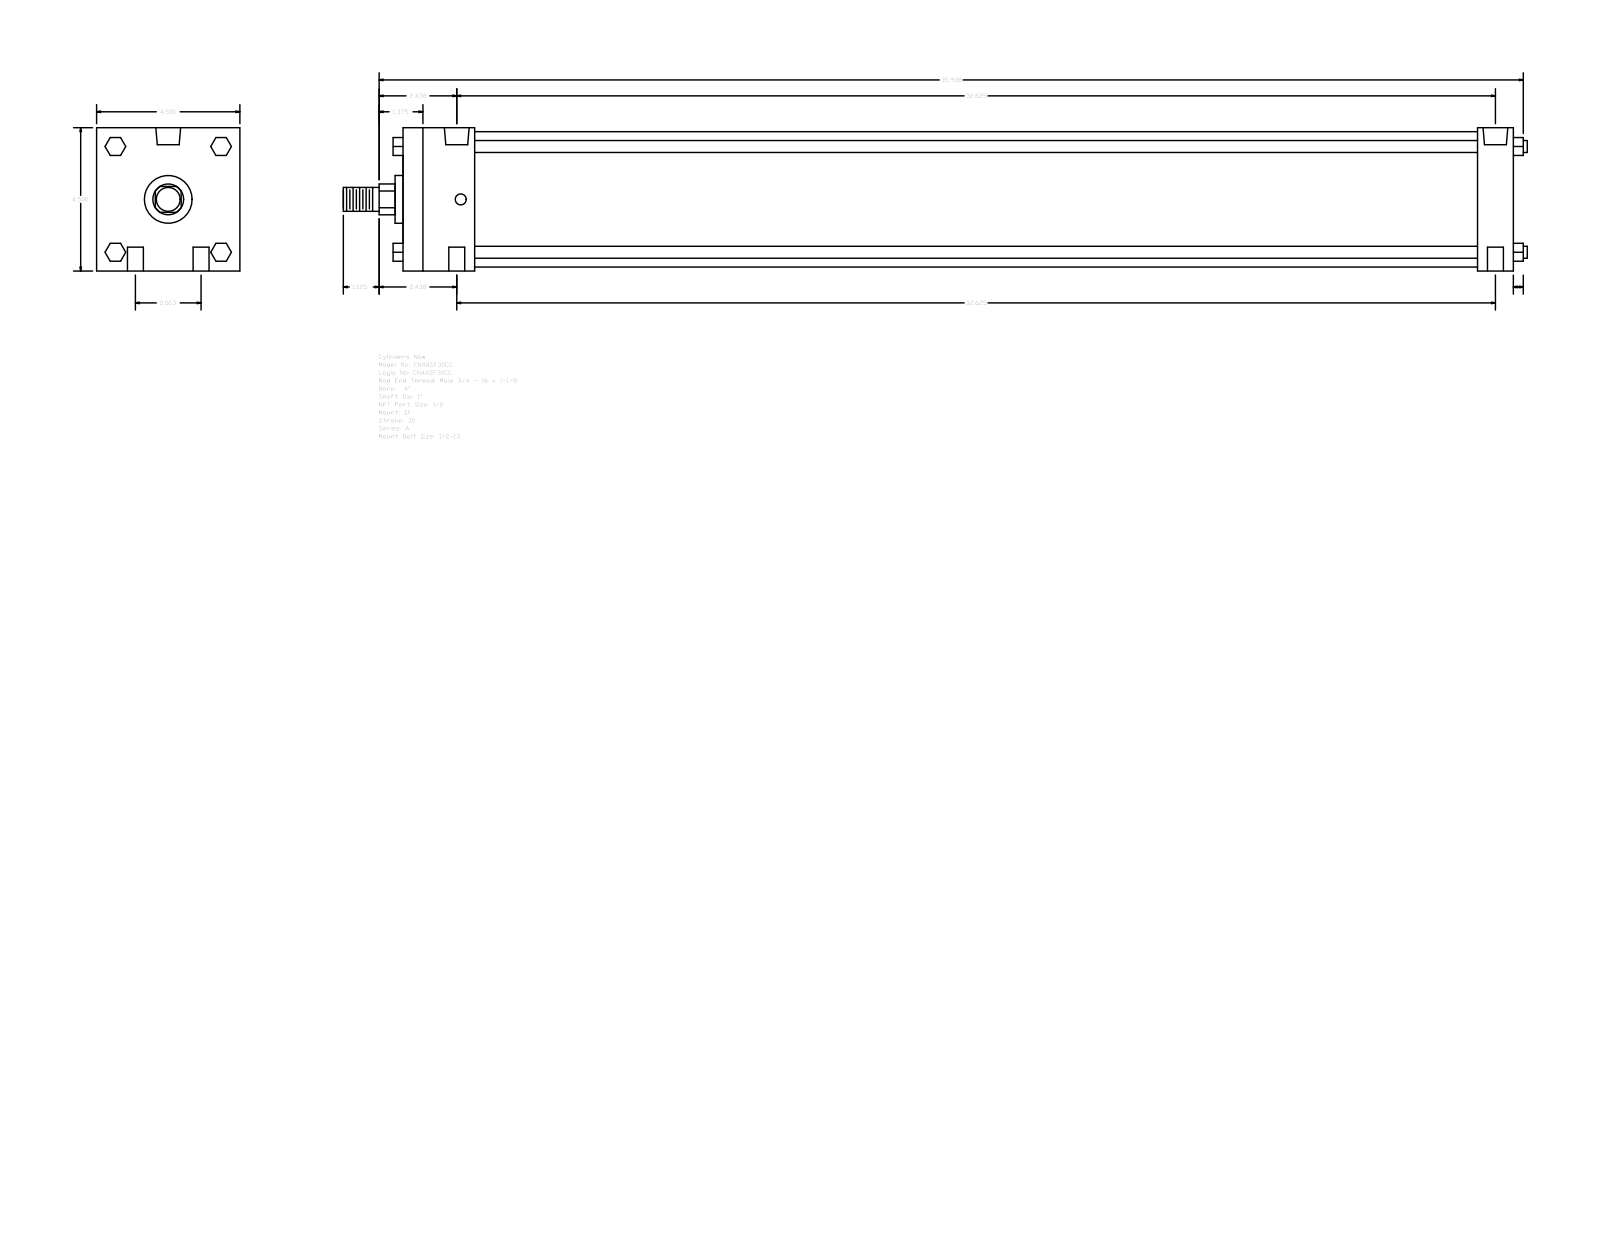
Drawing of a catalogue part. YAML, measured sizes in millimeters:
part_name: "A_SF__0400_1"
step_written_by: "GSSL Pune (CONFIG_CONTROL_DESIGN)"
units: millimeters
bodies: {solids: 0, faces: 124, planar: 94, cylindrical: 30, other: 0}
overall_size: [944.56, 114.3, 114.3]
round_holes:
  - {diameter: 12.7, count: 4}
  - {diameter: 8.73, count: 2}
  - {diameter: 19.77, count: 2}
round_bosses_or_shafts:
  - {diameter: 9.53, count: 4}
  - {diameter: 107.95, count: 1}
  - {diameter: 38.1, count: 1}
  - {diameter: 25.4, count: 1}
  - {diameter: 19.05, count: 1}
partial_cylinders:
  - {radius: 12.29, count: 1}
face_to_face_distances: [114.3, 885.83, 857.25, 28.58, 57.15, 800.1, 828.68, 14.29, 42.16, 73.03]
hole_center_spacings: [26.19, 829.09, 828.68, 52.38, 830.33, 822.32]
